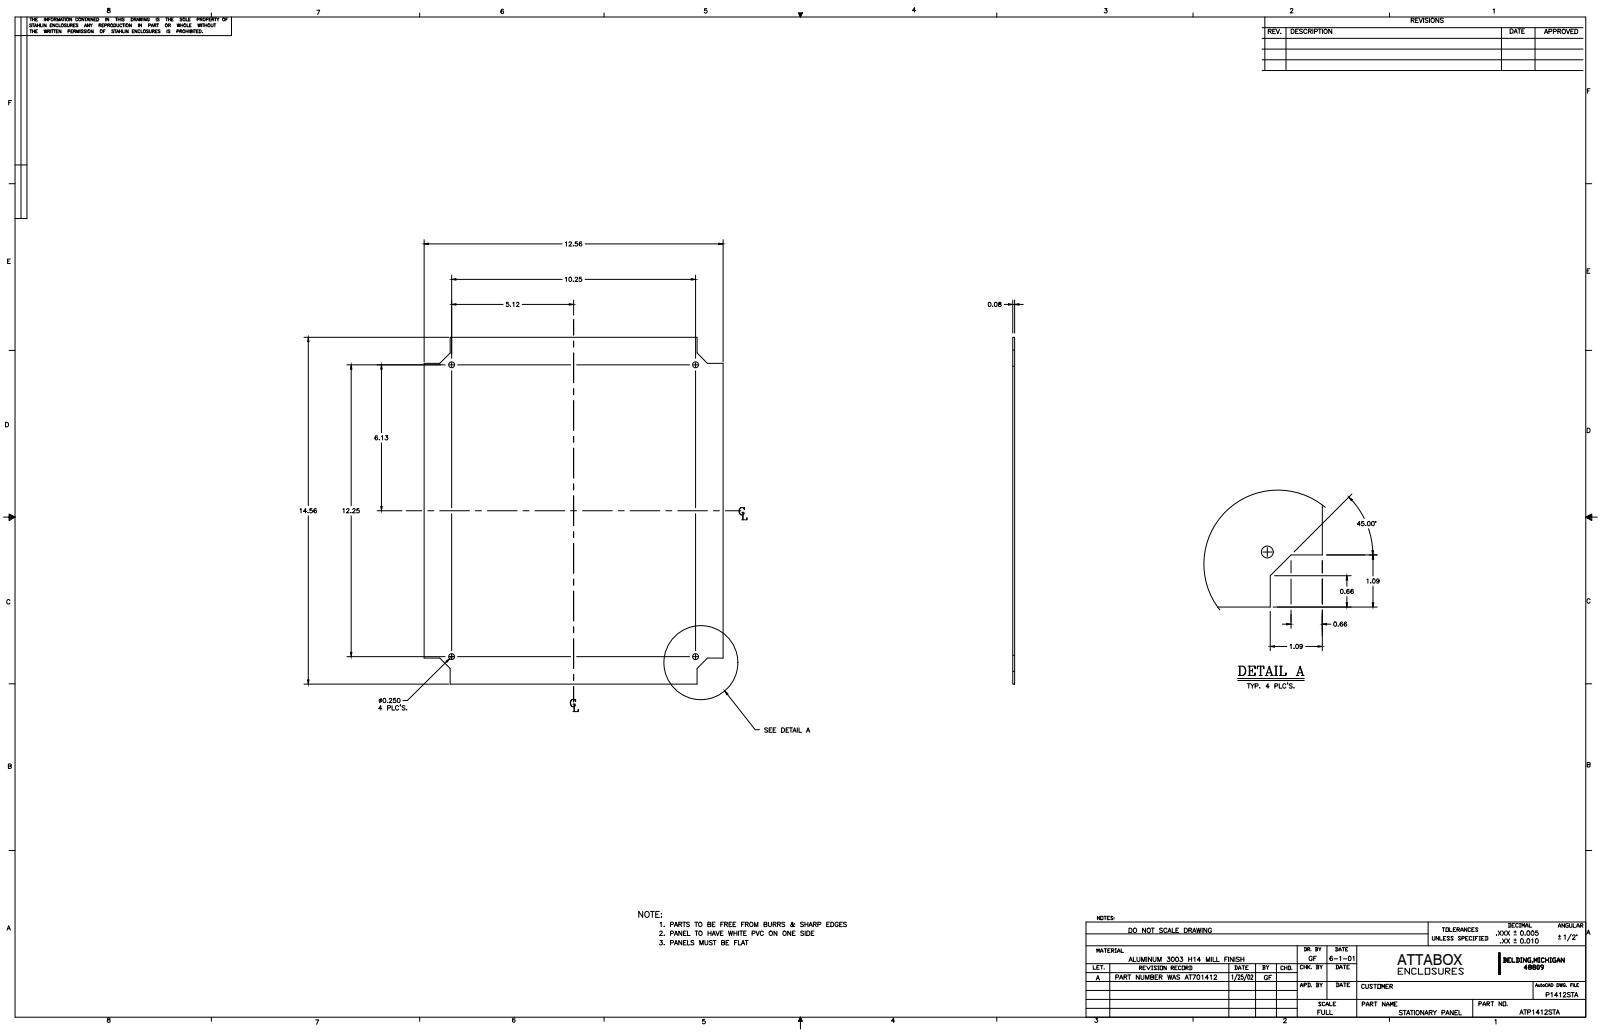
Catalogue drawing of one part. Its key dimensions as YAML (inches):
part_name: "P1412STAL"
step_written_by: "Autodesk Inventor 11 (AUTOMOTIVE_DESIGN)"
units: inches
bodies: {solids: 1, faces: 22, planar: 18, cylindrical: 4, other: 0}
overall_size: [14.563, 12.563, 0.08]
volume: 14.27
surface_area: 361.2
round_holes:
  - {diameter: 0.25, count: 4}
face_to_face_distances: [0.08, 12.562, 14.562, 1.094, 11.468, 13.468, 10.374, 12.374, 16.701]
hole_center_spacings: [10.25, 12.25, 15.972, 15.973]
